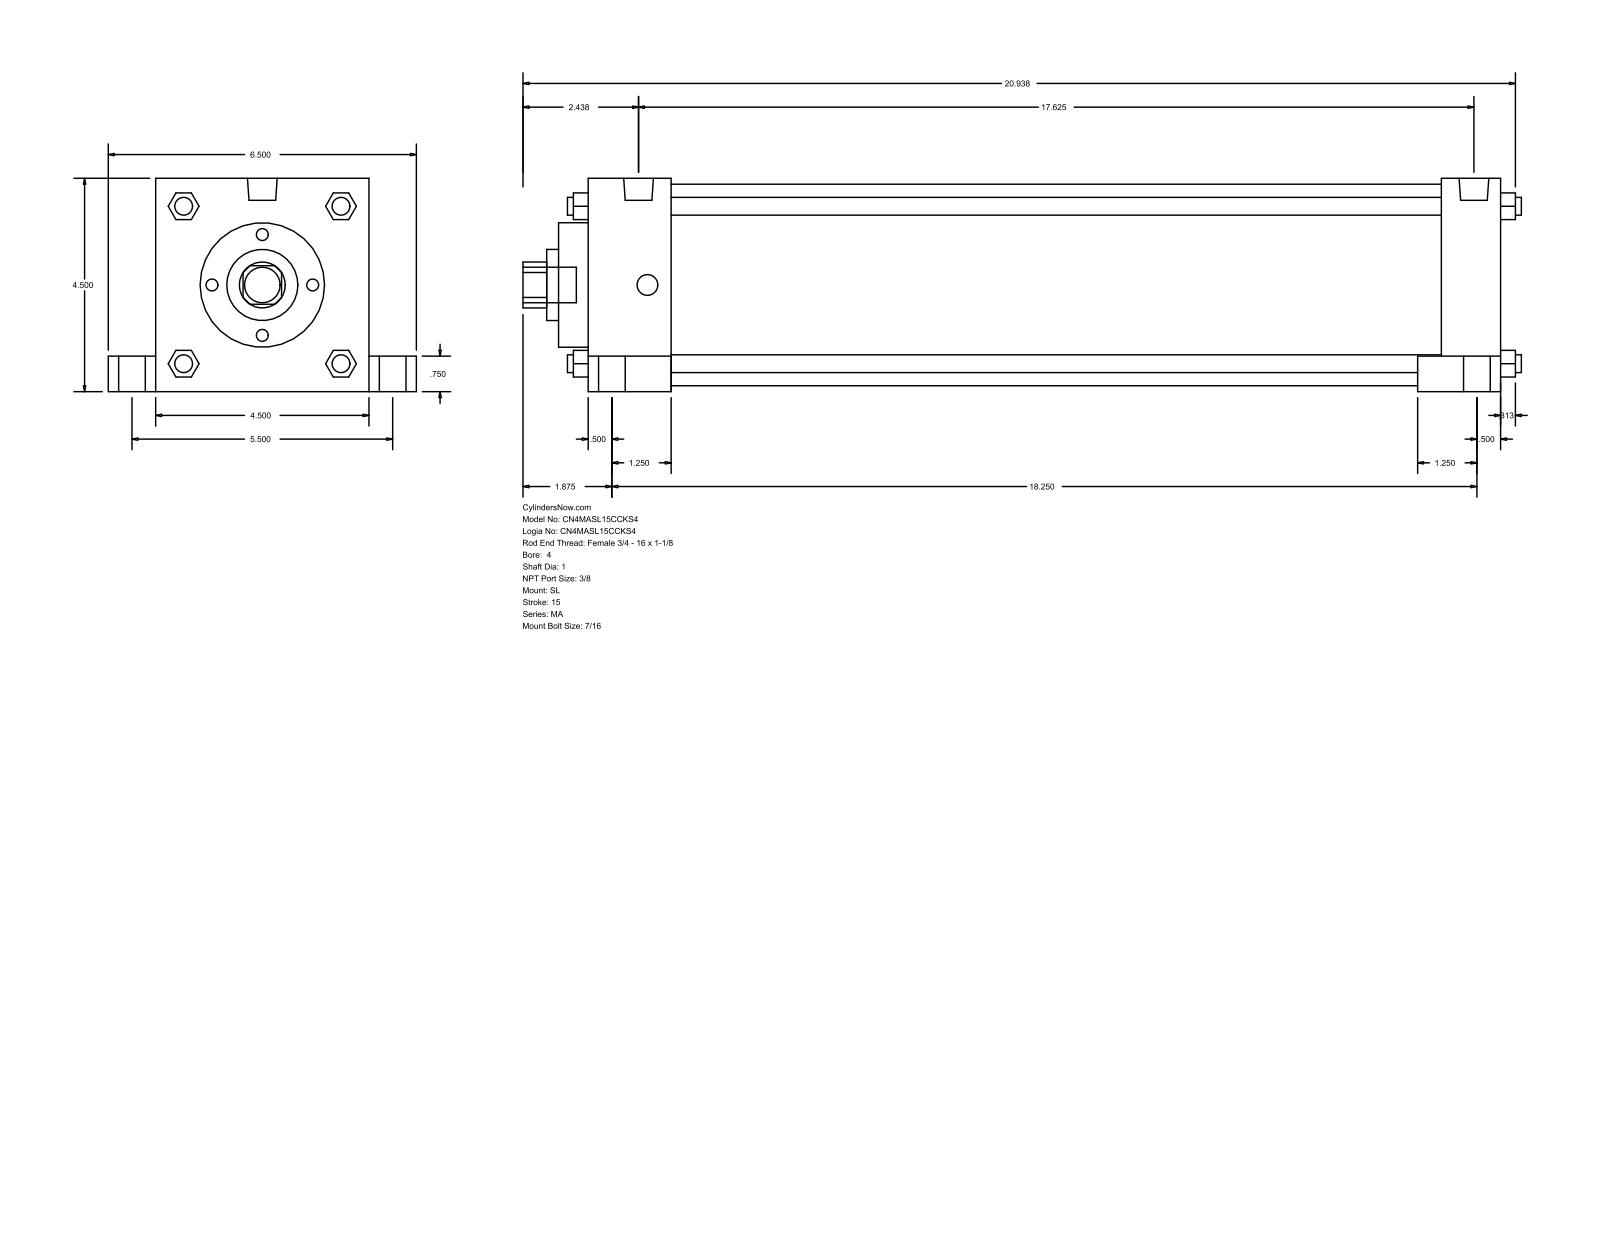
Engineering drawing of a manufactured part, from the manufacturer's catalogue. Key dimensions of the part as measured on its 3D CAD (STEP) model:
Part name (STEP PRODUCT): MA_SL__0400_1
STEP written by: GSSL Pune (CONFIG_CONTROL_DESIGN)
Units: millimetres
Bodies: 0 solids, 150 faces (113 planar, 37 cylindrical, 0 other)
Overall size (bounding box): 534.99 × 165.1 × 114.3
Round holes (diameter × count): ⌀25.4 ×1, ⌀38.1 ×1, ⌀66.67 ×1, ⌀107.95 ×1
Round bosses / shafts (diameter × count): ⌀20.64 ×4, ⌀14.29 ×4, ⌀11.11 ×4, ⌀9.53 ×4, ⌀15.93 ×2, ⌀19.05 ×1
Partial cylindrical surfaces — rounded edges, fillets, slot ends (radius × count): R12.29 ×1
Main face-to-face distances: 114.3, 488.96, 44.46, 444.5, 457.2, 412.74, 31.76, 25.4, 139.7, 19.05
